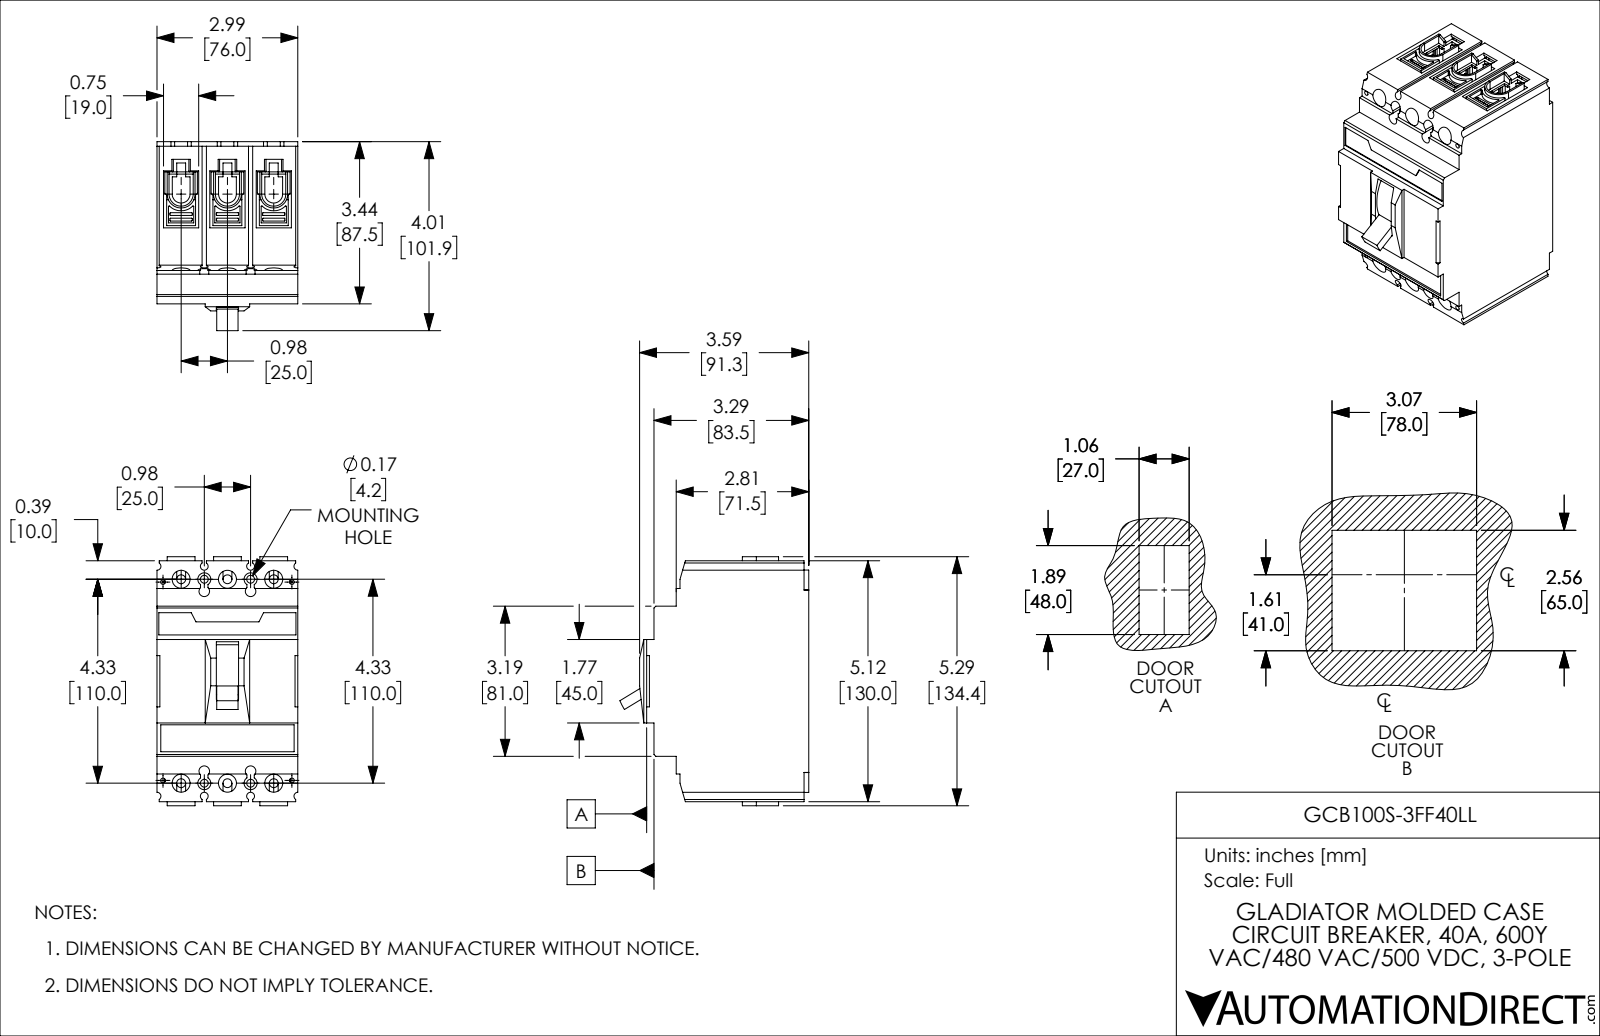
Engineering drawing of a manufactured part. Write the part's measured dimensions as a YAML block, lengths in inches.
part_name: "GCB100S-3FF40LL"
step_written_by: "SolidWorks 2021 (CONFIG_CONTROL_DESIGN)"
units: inches
bodies: {solids: 1, faces: 1256, planar: 784, cylindrical: 424, other: 48}
overall_size: [5.291, 4.013, 2.992]
volume: 43.23
surface_area: 148.5
round_holes:
  - {diameter: 0.165, count: 8}
  - {diameter: 0.189, count: 6}
  - {diameter: 0.382, count: 6}
  - {diameter: 0.098, count: 4}
  - {diameter: 0.276, count: 4}
partial_cylinders:
  - {radius: 0.012, count: 86}
  - {radius: 0.02, count: 38}
  - {radius: 0.039, count: 14}
  - {radius: 0.157, count: 14}
  - {radius: 0.024, count: 6}
  - {radius: 0.083, count: 4}
  - {radius: 0.112, count: 4}
  - {radius: 0.189, count: 3}
face_to_face_distances: [2.992, 0.984, 0.622, 4.496, 1.732, 0.11, 3.445, 0.748, 1.969, 5.118]
hole_center_spacings: [0.492, 0.564, 0.984, 4.359, 4.633, 4.441, 4.331, 0.276]
